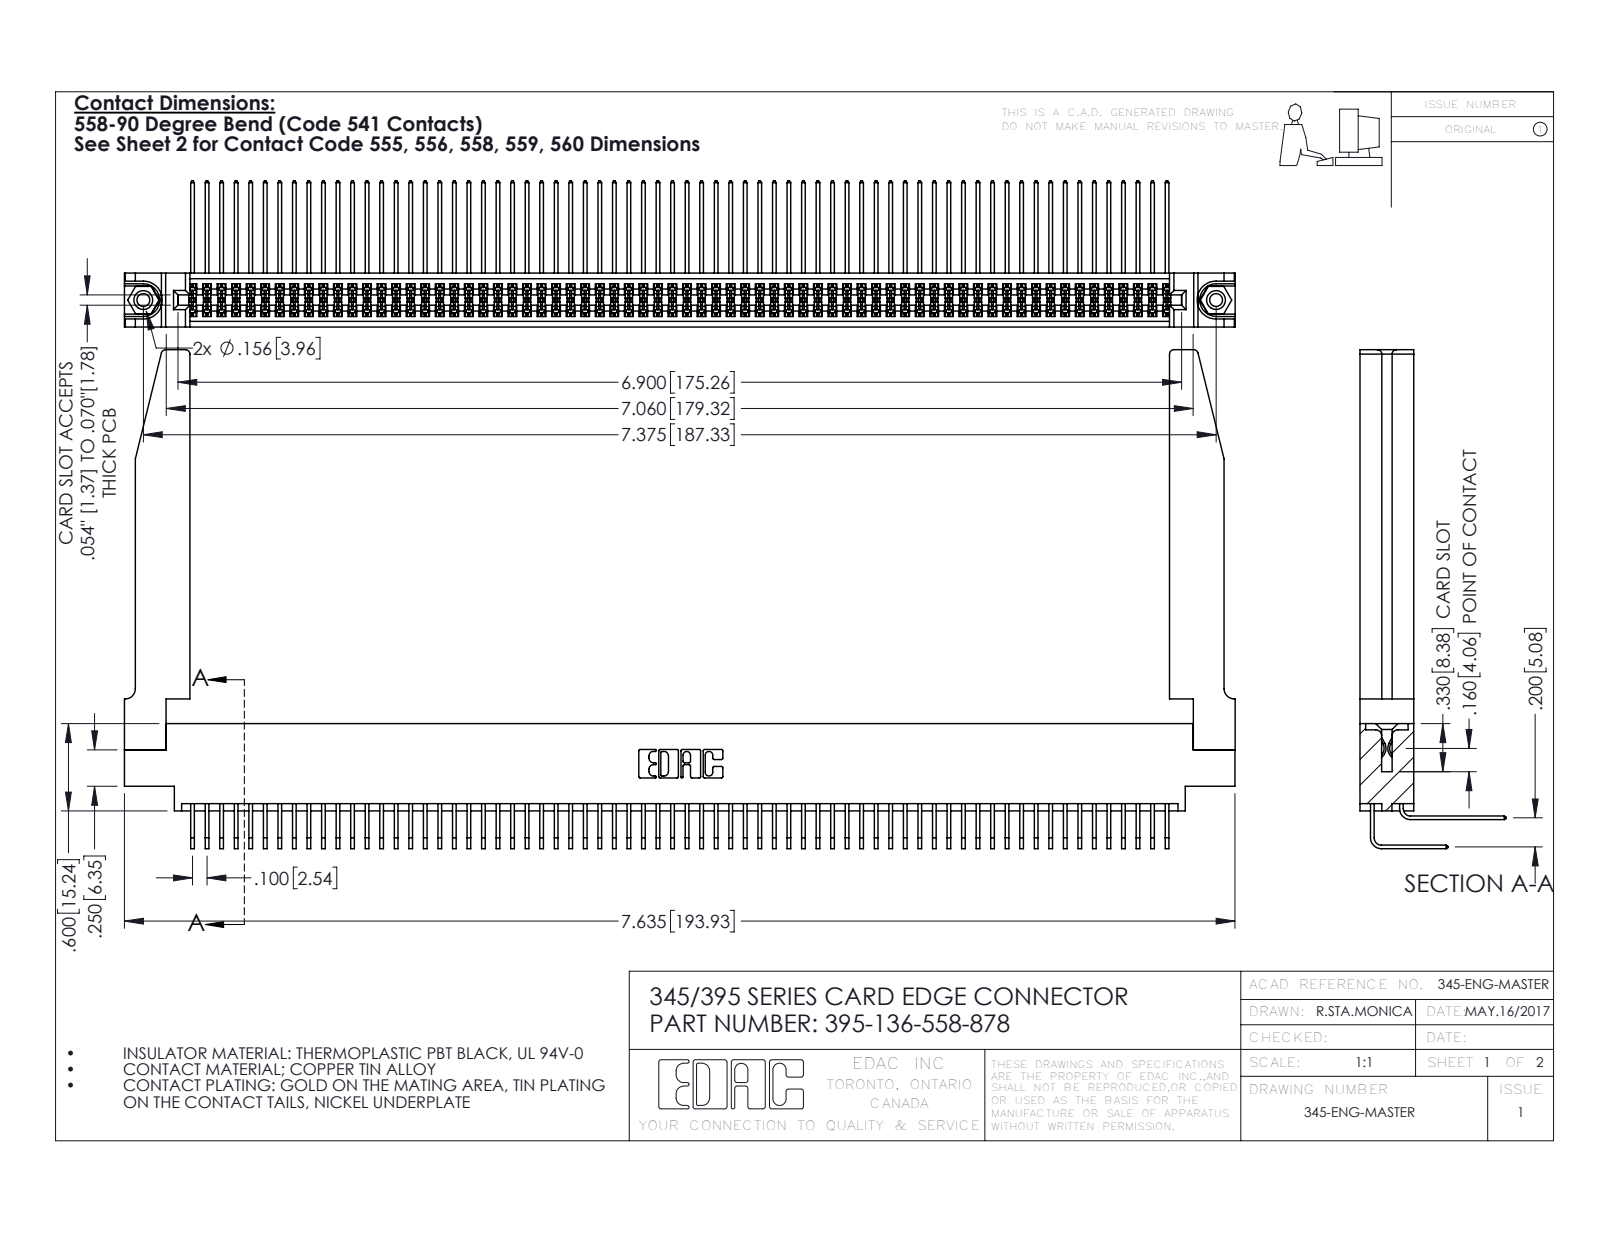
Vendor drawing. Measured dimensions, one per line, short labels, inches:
name: 345-250-001_345-250-001-102; 345 Part_0.170 Offset - 0.156 Dia-TH; 345-292-001_558 Tail - 2; 345-220-078_345-220-078 (+2 more)
written by: SolidWorks 2016 (CONFIG_CONTROL_DESIGN)
unit: in
bodies: 141 solids, 7436 faces (4986 planar, 2398 cylindrical, 52 other)
size: 7.636 × 3.429 × 1.005
volume: 1.68 in³; area: 62.58 in²
holes: 2× ⌀0.089, 2× ⌀0.125, 2× ⌀0.156, 1× ⌀0.064
bosses: 2× ⌀0.155
rounds: 271× R0.006, 22× R0.01, 8× R0.03, 6× R0.007, 6× R0.031, 3× R0.026, 2× R0.014, 2× R0.019
face distances: 0.072, 0.298, 0.37, 0.2, 0.098, 0.272, 0.025, 0.225, 0.175, 0.025
hole spacings: 0.27, 7.139, 7.375
